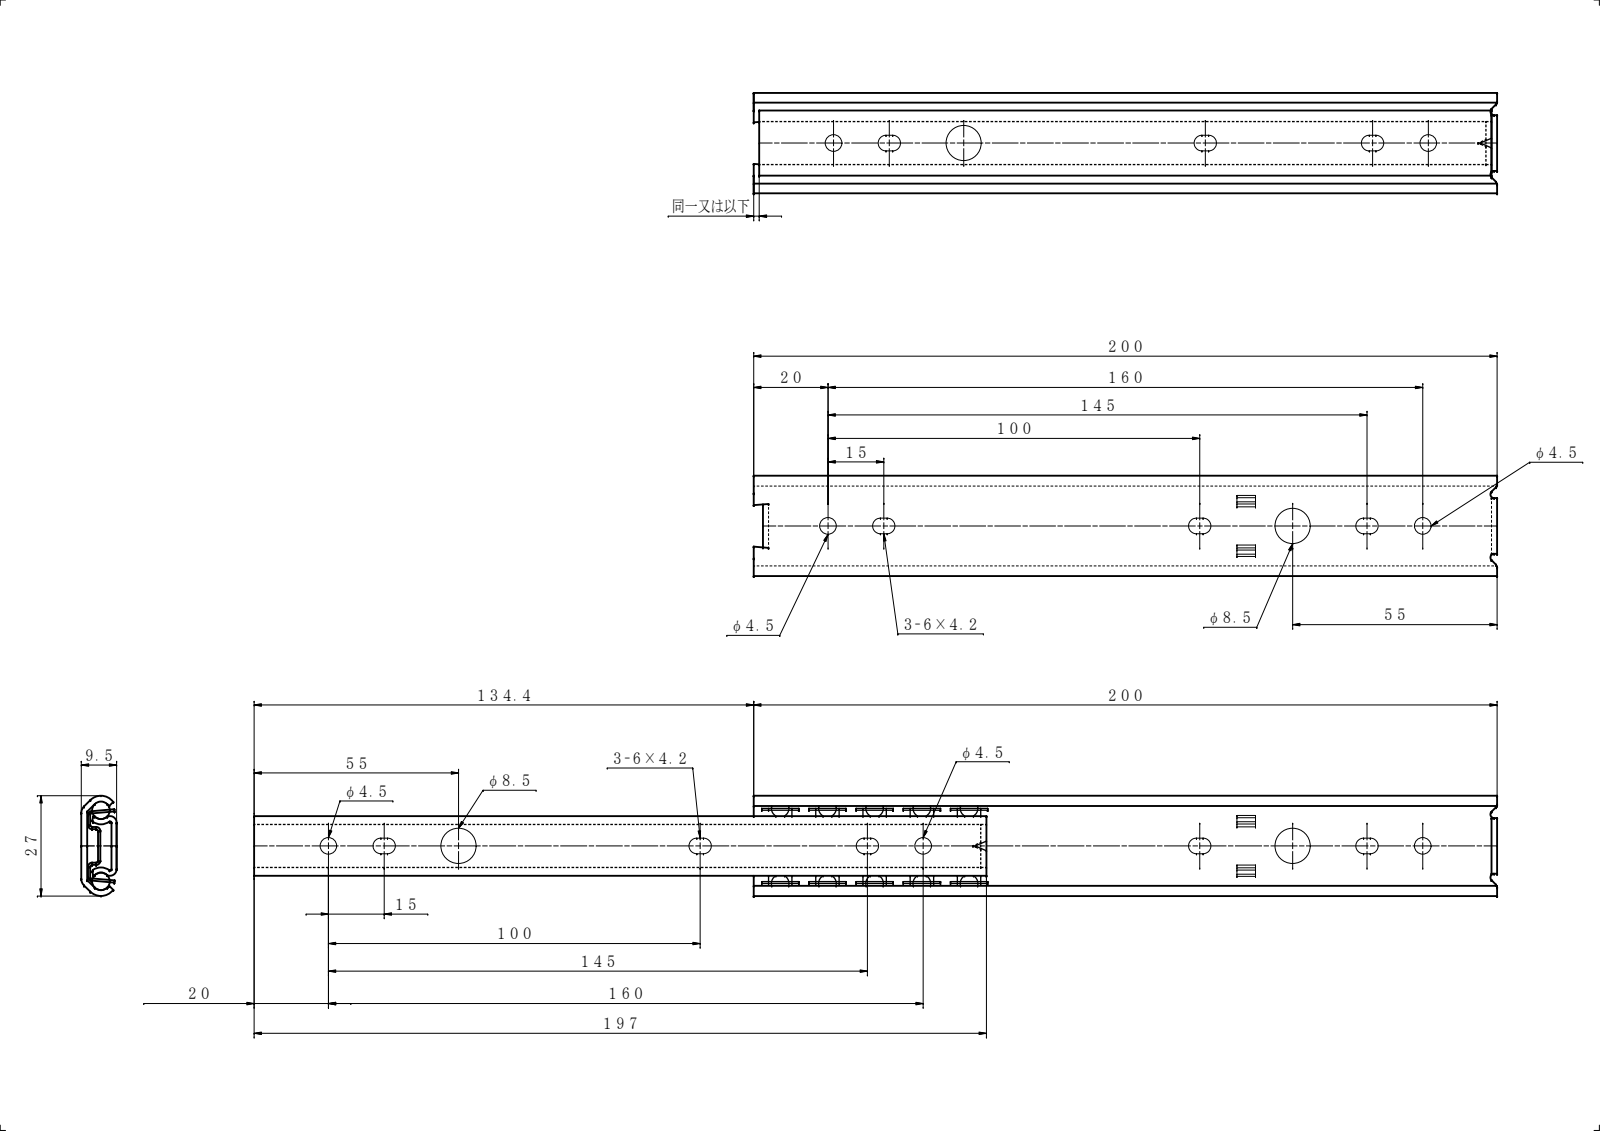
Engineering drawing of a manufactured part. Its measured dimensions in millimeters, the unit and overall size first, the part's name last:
Units: millimetres
Overall size (bounding box): 334.4 × 27 × 9.5
Round holes (diameter × count): ⌀4.5 ×4, ⌀8.5 ×2
Partial cylindrical surfaces — rounded edges, fillets, slot ends (radius × count): R2.1 ×12, R2 ×10, R1 ×8, R0.28 ×2, R1.68 ×2, R2.38 ×2, R3 ×2, R3.78 ×2
Main face-to-face distances: 1.6, 1.4, 9.5, 7.9, 8.1, 6.5, 196, 137.4, 135.8, 197.6
Hole centre spacings: 35, 99.4, 125, 134.4, 160, 259.4, 25.6, 224.4
Volume: 18 583 mm³ · Surface area: 26 355 mm²
Bodies: 2 solids, 116 faces (53 planar, 63 cylindrical, 0 other)
Part name (STEP PRODUCT): 2721-200; OM-2721-200; IM-2721-200
STEP written by: SolidWorks 2019 (CONFIG_CONTROL_DESIGN)
